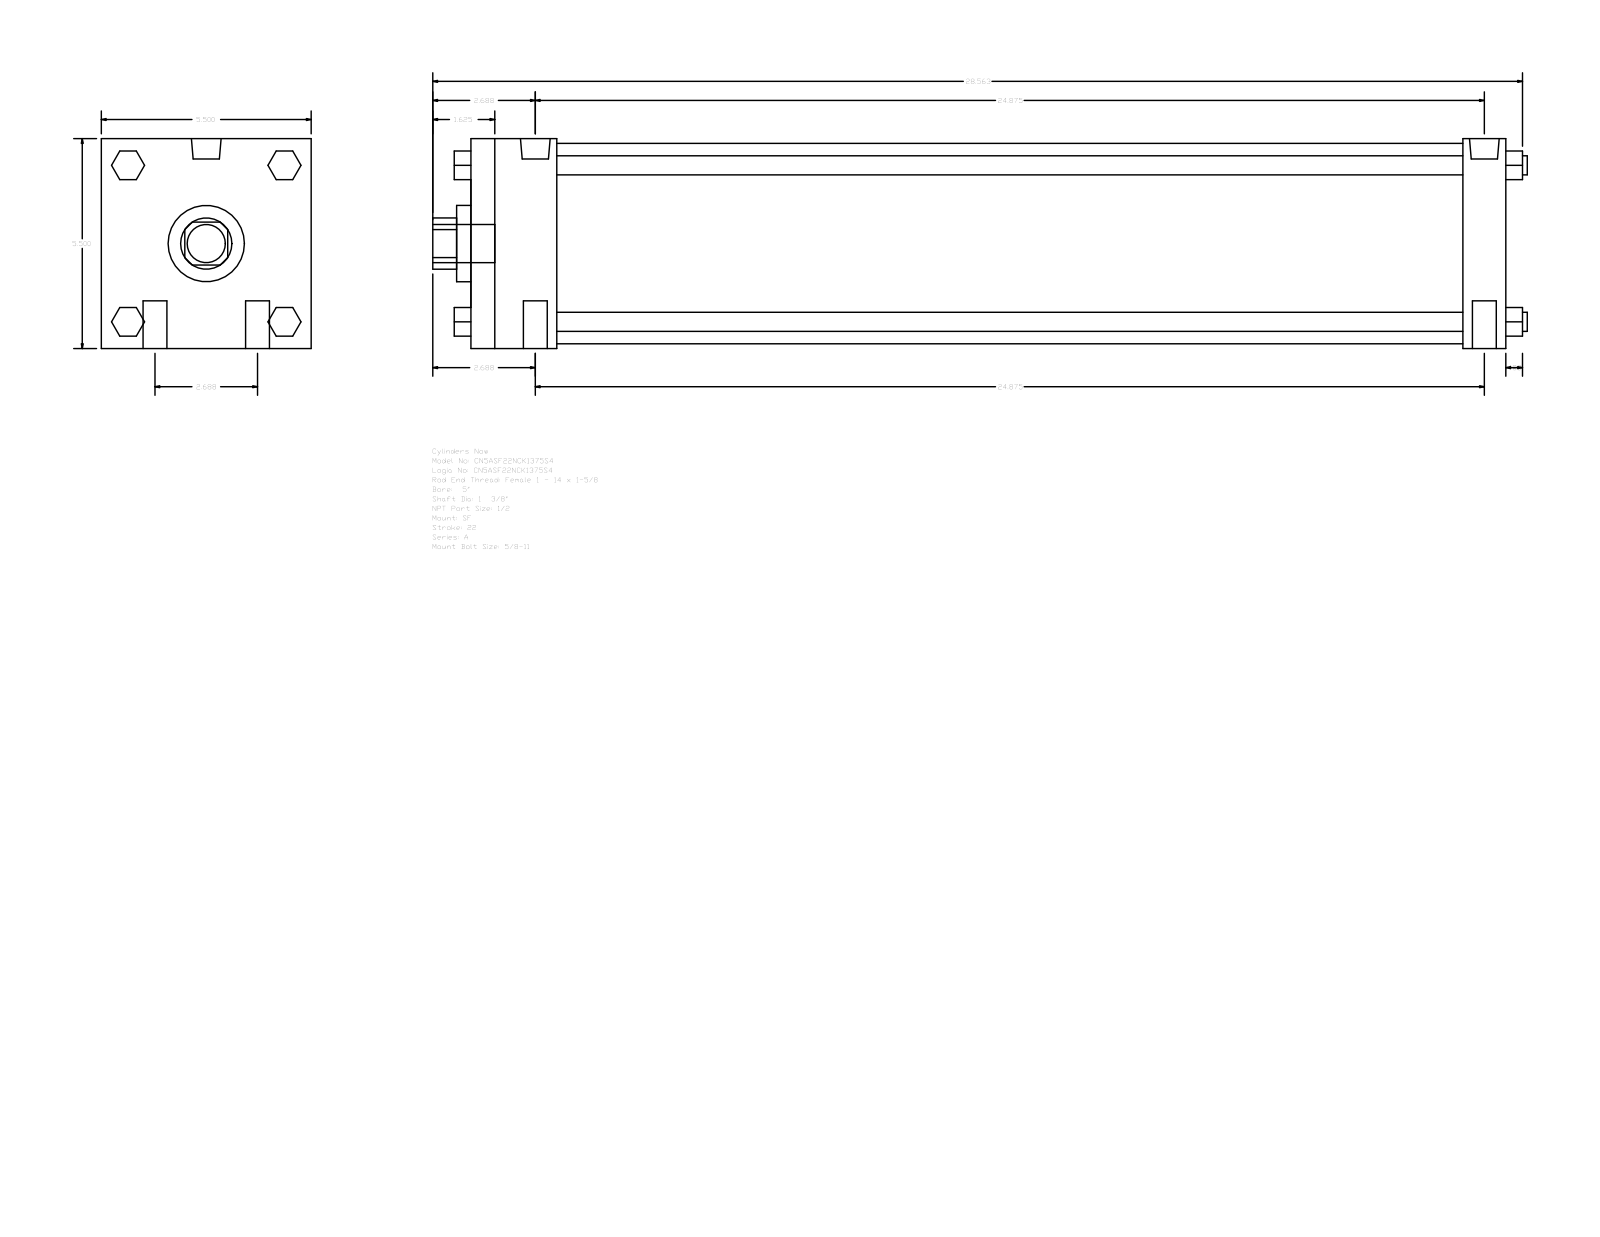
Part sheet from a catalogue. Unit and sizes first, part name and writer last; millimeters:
Units: millimetres
Overall size (bounding box): 728.66 × 139.7 × 139.7
Round holes (diameter × count): ⌀34.92 ×1, ⌀50.8 ×1, ⌀133.35 ×1
Round bosses / shafts (diameter × count): ⌀15.88 ×4, ⌀12.7 ×4, ⌀19.77 ×2, ⌀8.73 ×2, ⌀25.4 ×1
Partial cylindrical surfaces — rounded edges, fillets, slot ends (radius × count): R17.06 ×1
Main face-to-face distances: 139.7, 688.98, 28.58, 57.15, 660.4, 603.25, 631.83, 19.05, 52.07, 90.18
Bodies: 0 solids, 124 faces (94 planar, 30 cylindrical, 0 other)
Part name (STEP PRODUCT): A_SF__0500_1.375
STEP written by: GSSL Pune (CONFIG_CONTROL_DESIGN)
